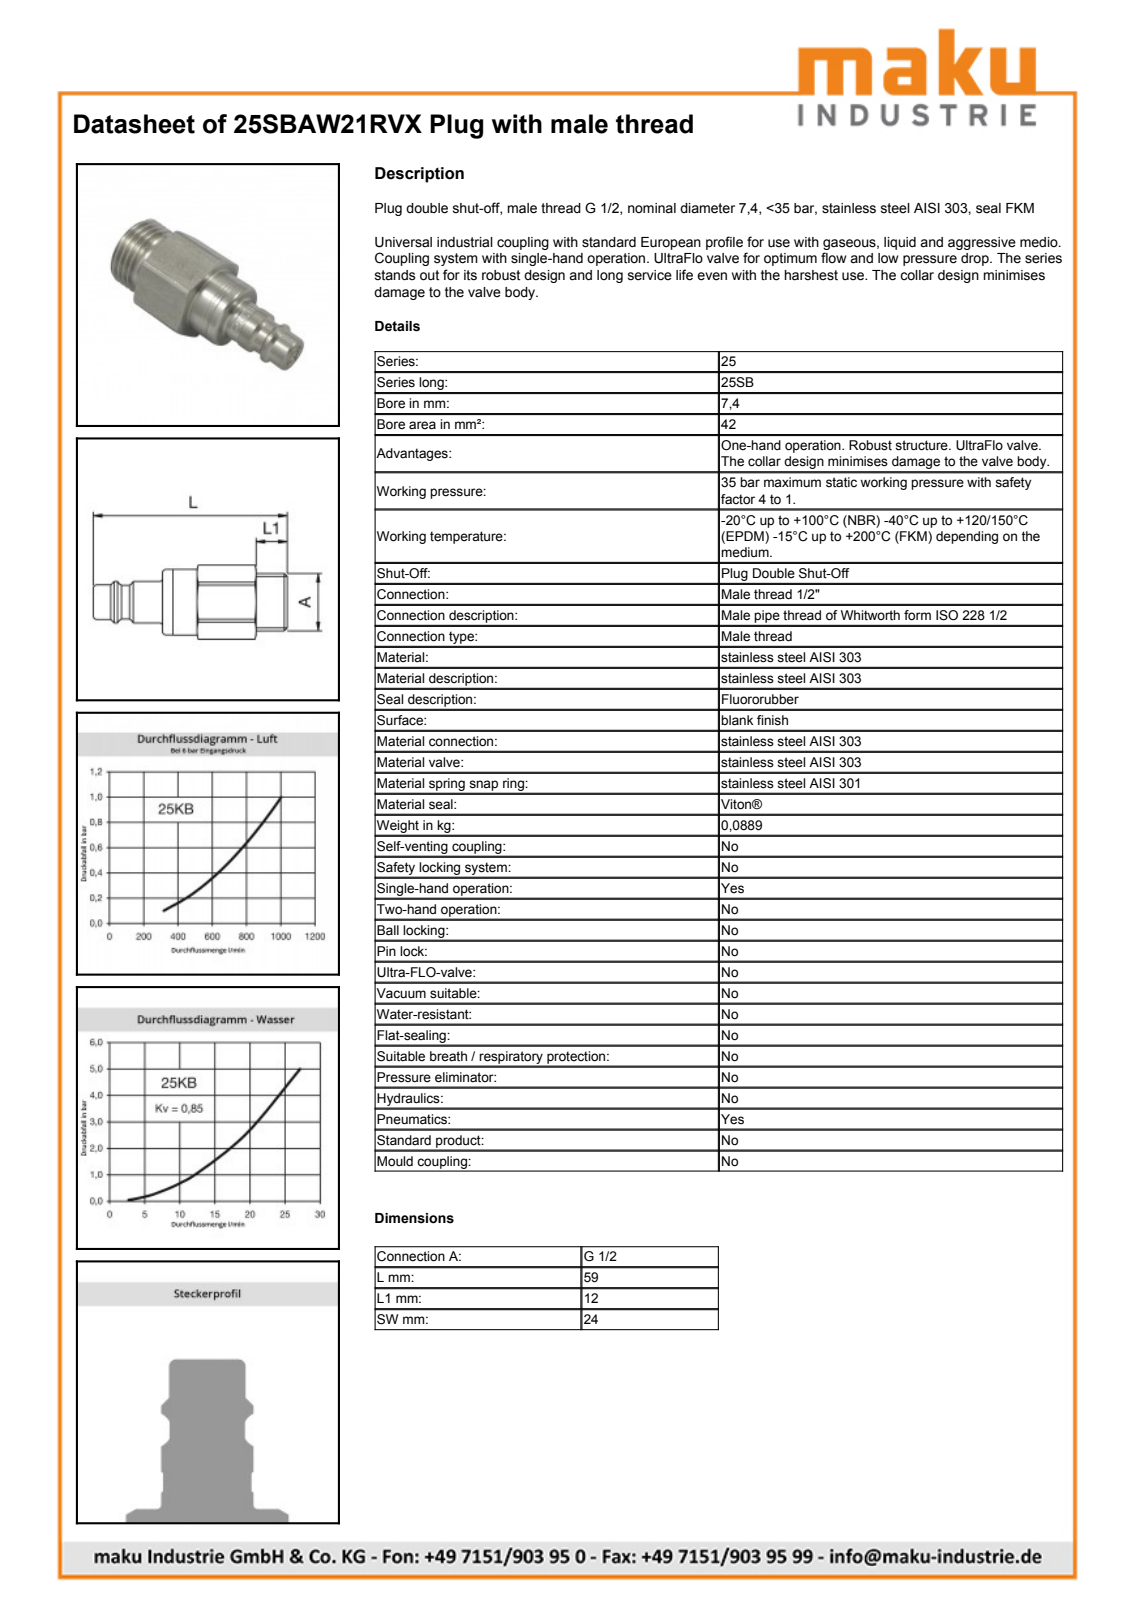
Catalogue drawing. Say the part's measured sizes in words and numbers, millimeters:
The part is named "D110440". Its 3-D file was written by "Autodesk Inventor 2013 (AUTOMOTIVE_DESIGN)". It is 1 solid with 47 faces: 12 planar, 13 cylindrical and 22 other. Overall it measures 59 by 26.77 by 25.91 millimeters. Its volume is 17 083 cubic millimeters and its surface area 4 411 square millimeters. Round bosses or shafts: 1 of diameter 20.96, 1 of diameter 19, 1 of diameter 18.95, 1 of diameter 12, 1 of diameter 9.9, 1 of diameter 9.75. Partial cylindrical surfaces (rounded edges, fillets, slot ends): 1 of radius 13.53. The main face-to-face distances are 24, 29.05, 17.05, 12, 9.95, 27, 39, 20, 29.95, 47.
